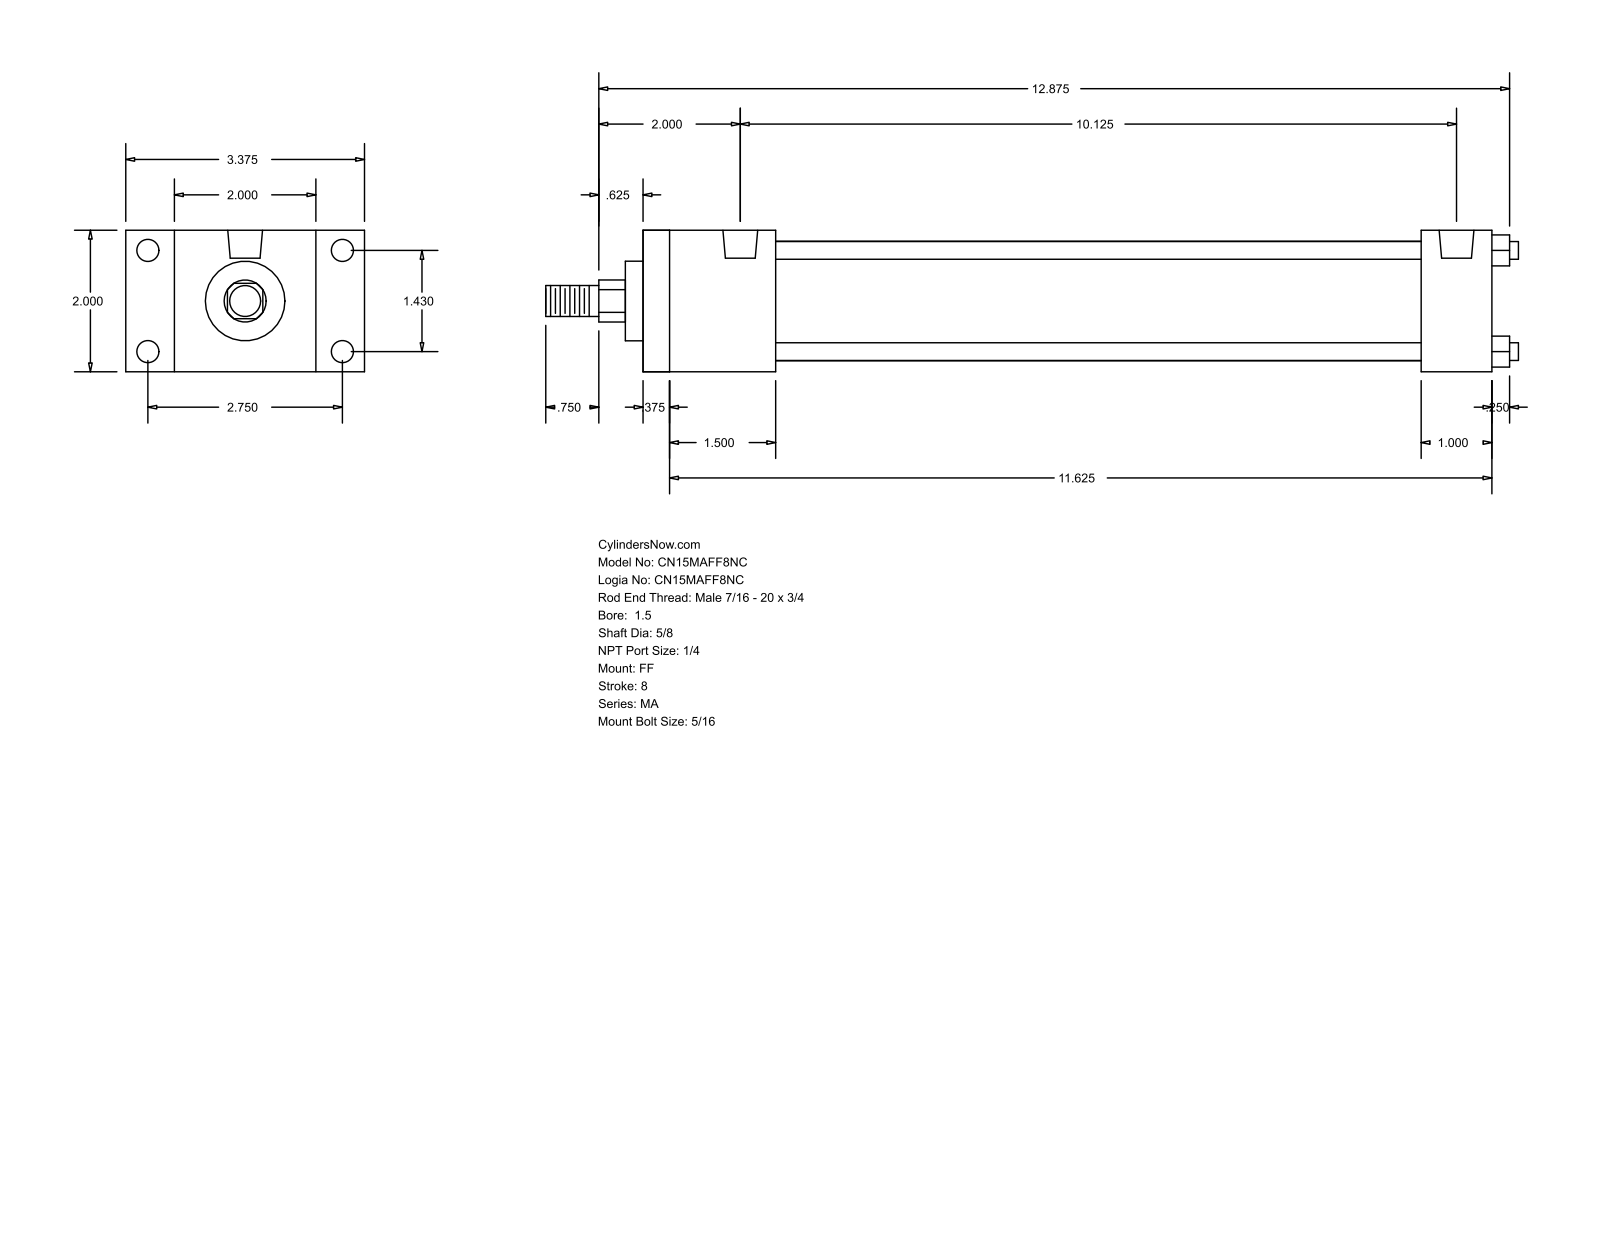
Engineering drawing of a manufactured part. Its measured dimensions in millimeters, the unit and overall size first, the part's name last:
Units: millimetres
Overall size (bounding box): 349.25 × 85.72 × 50.8
Round holes (diameter × count): ⌀7.94 ×8, ⌀12.49 ×2
Round bosses / shafts (diameter × count): ⌀6.35 ×4, ⌀42.93 ×1, ⌀28.57 ×1, ⌀15.88 ×1, ⌀11.11 ×1
Partial cylindrical surfaces — rounded edges, fillets, slot ends (radius × count): R7.54 ×1
Main face-to-face distances: 50.8, 304.8, 9.52, 295.28, 47.62, 279.39, 38.1, 269.87, 231.77, 257.18
Hole centre spacings: 36.32, 69.84, 78.72, 257.18
Bodies: 0 solids, 92 faces (64 planar, 28 cylindrical, 0 other)
Part name (STEP PRODUCT): MA_FF__0150_0.625
STEP written by: GSSL Pune (CONFIG_CONTROL_DESIGN)
